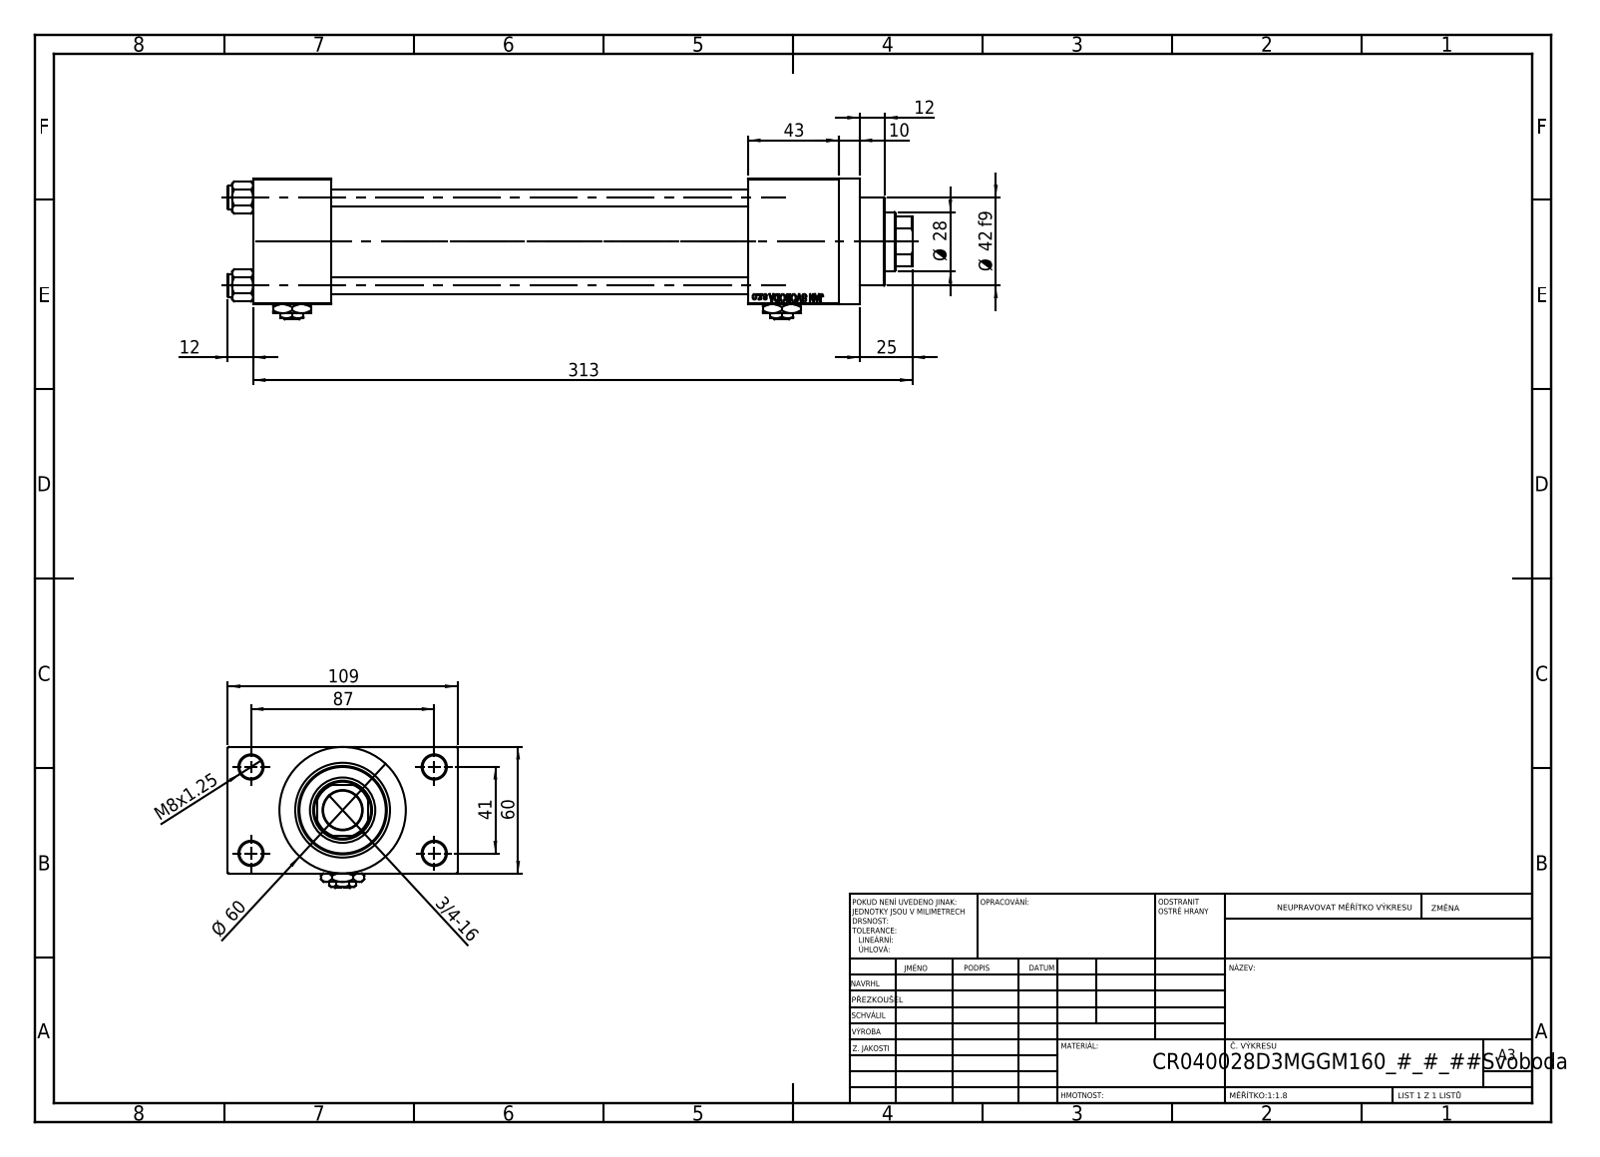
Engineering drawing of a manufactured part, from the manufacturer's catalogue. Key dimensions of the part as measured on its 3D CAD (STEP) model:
Part name (STEP PRODUCT): V215CR_D_Body; V215CR_D_TYCINKA; V215CR_VCP_D; Zatka_pro_OIL_PORT (+2 more)
STEP written by: SolidWorks 2019 (CONFIG_CONTROL_DESIGN)
Units: millimetres
Bodies: 13 solids, 1206 faces (546 planar, 100 cylindrical, 560 other)
Overall size (bounding box): 325 × 109 × 67
Volume: 703 037 mm³ · Surface area: 194 689 mm²
Round holes (diameter × count): ⌀8 ×4, ⌀11 ×4, ⌀7 ×2, ⌀16.66 ×2, ⌀24 ×2, ⌀18.5 ×1, ⌀28 ×1, ⌀31 ×1, ⌀40 ×1, ⌀45 ×1
Round bosses / shafts (diameter × count): ⌀11 ×4, ⌀60 ×1, ⌀46 ×1, ⌀42 ×1
Partial cylindrical surfaces — rounded edges, fillets, slot ends (radius × count): R13.5 ×1
Main face-to-face distances: 60, 24.5, 84.5, 198, 37, 235, 278, 241, 43, 109
Hole centre spacings: 22.65, 29.49, 41.7, 47.15, 48.09, 64.35, 76.49, 41
